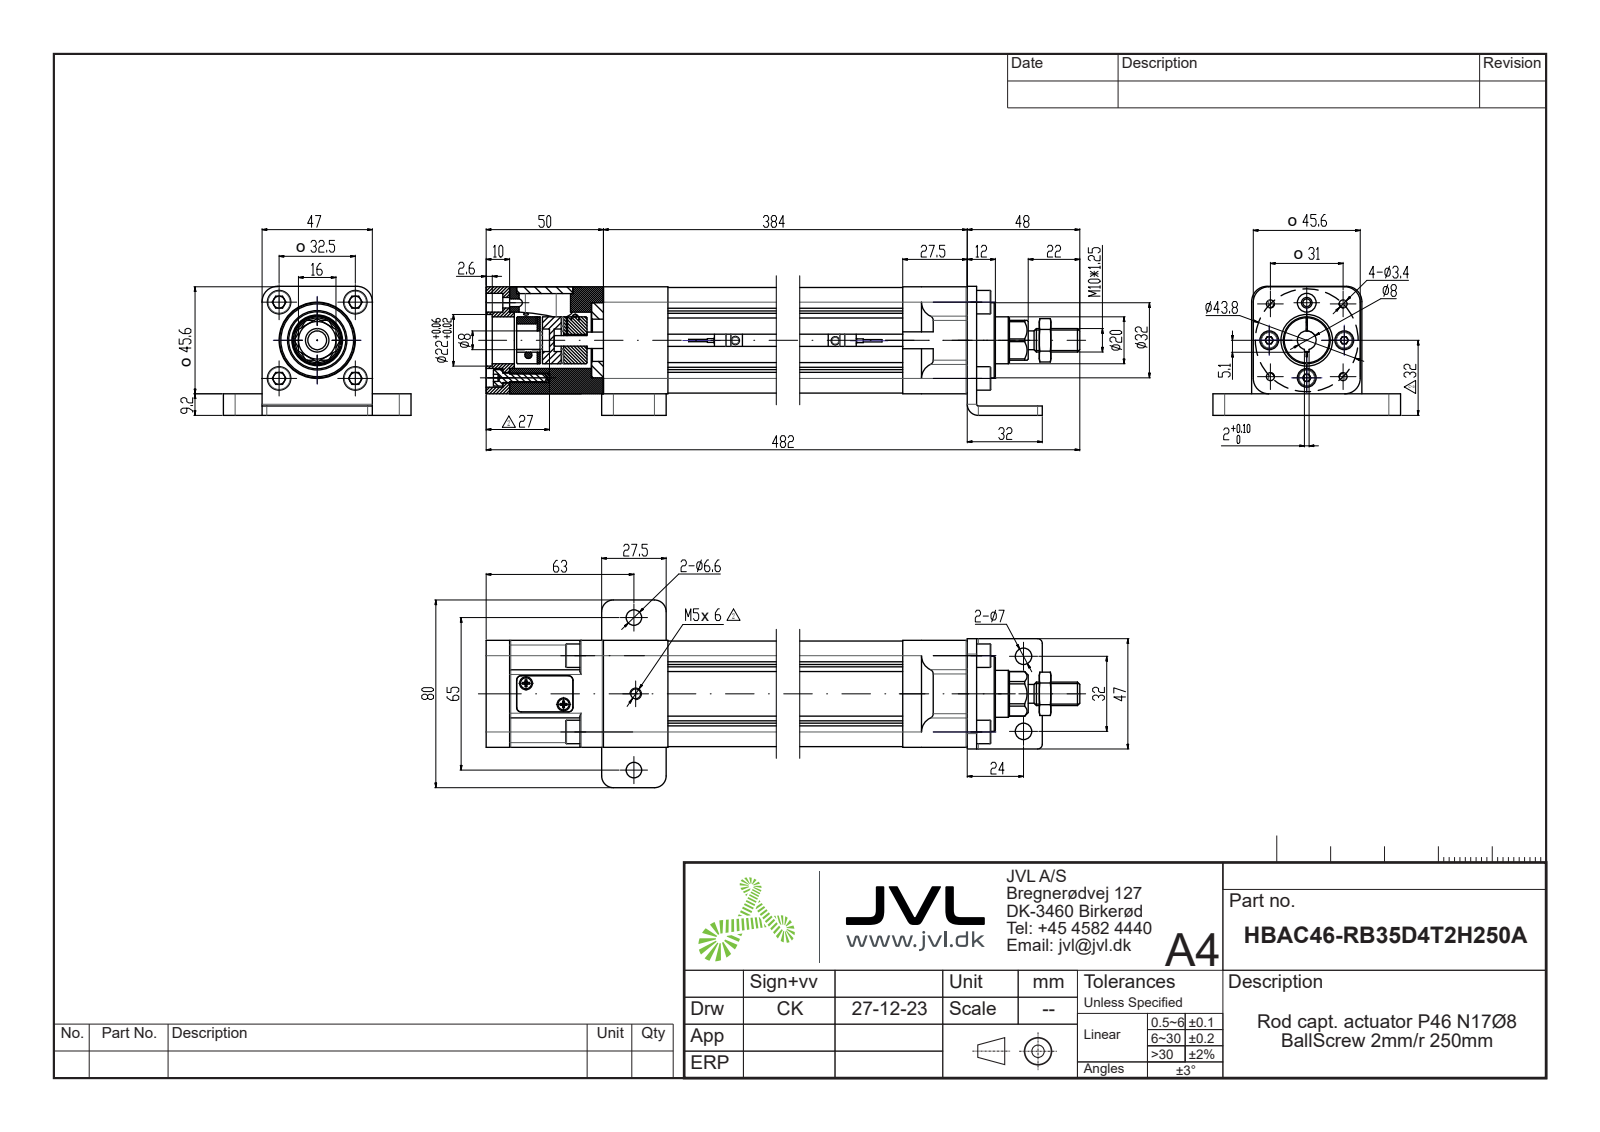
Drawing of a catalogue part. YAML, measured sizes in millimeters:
part_name: "2014-250; hex thin nuts-grades ab-chamfered gb_GB_FASTENER_NUT_STNAB M10-S; HBAC46-RB35D4T2H250A; AOE-32-1-2-250 (+8 more)"
step_written_by: "SolidWorks 2023 (AUTOMOTIVE_DESIGN)"
units: millimeters
bodies: {solids: 63, faces: 2603, planar: 856, cylindrical: 837, other: 910}
overall_size: [482, 80, 55]
volume: 627552
surface_area: 301511
round_holes:
  - {diameter: 3.4, count: 8}
  - {diameter: 2.5, count: 7}
  - {diameter: 6.6, count: 6}
  - {diameter: 3.3, count: 4}
  - {diameter: 4.5, count: 4}
  - {diameter: 5, count: 4}
  - {diameter: 6.4, count: 4}
  - {diameter: 6.5, count: 4}
  - {diameter: 8, count: 4}
  - {diameter: 9.5, count: 4}
  - {diameter: 2.05, count: 2}
  - {diameter: 2.9, count: 2}
round_bosses_or_shafts:
  - {diameter: 3, count: 7}
  - {diameter: 5.5, count: 6}
  - {diameter: 7, count: 5}
  - {diameter: 10, count: 4}
  - {diameter: 9, count: 4}
  - {diameter: 6, count: 4}
  - {diameter: 4, count: 4}
  - {diameter: 5, count: 3}
partial_cylinders:
  - {radius: 0.16, count: 36}
  - {radius: 2, count: 26}
  - {radius: 0.5, count: 20}
  - {radius: 6, count: 17}
  - {radius: 1, count: 12}
  - {radius: 0.1, count: 6}
  - {radius: 5, count: 6}
  - {radius: 6.55, count: 6}
face_to_face_distances: [45, 45.3, 41.8, 40.5, 4.5, 4.8, 27.5, 19.5, 3.5, 19.1]
hole_center_spacings: [15.51, 16.25, 31.76, 35.11, 36.11, 16, 32.5, 1.06]
